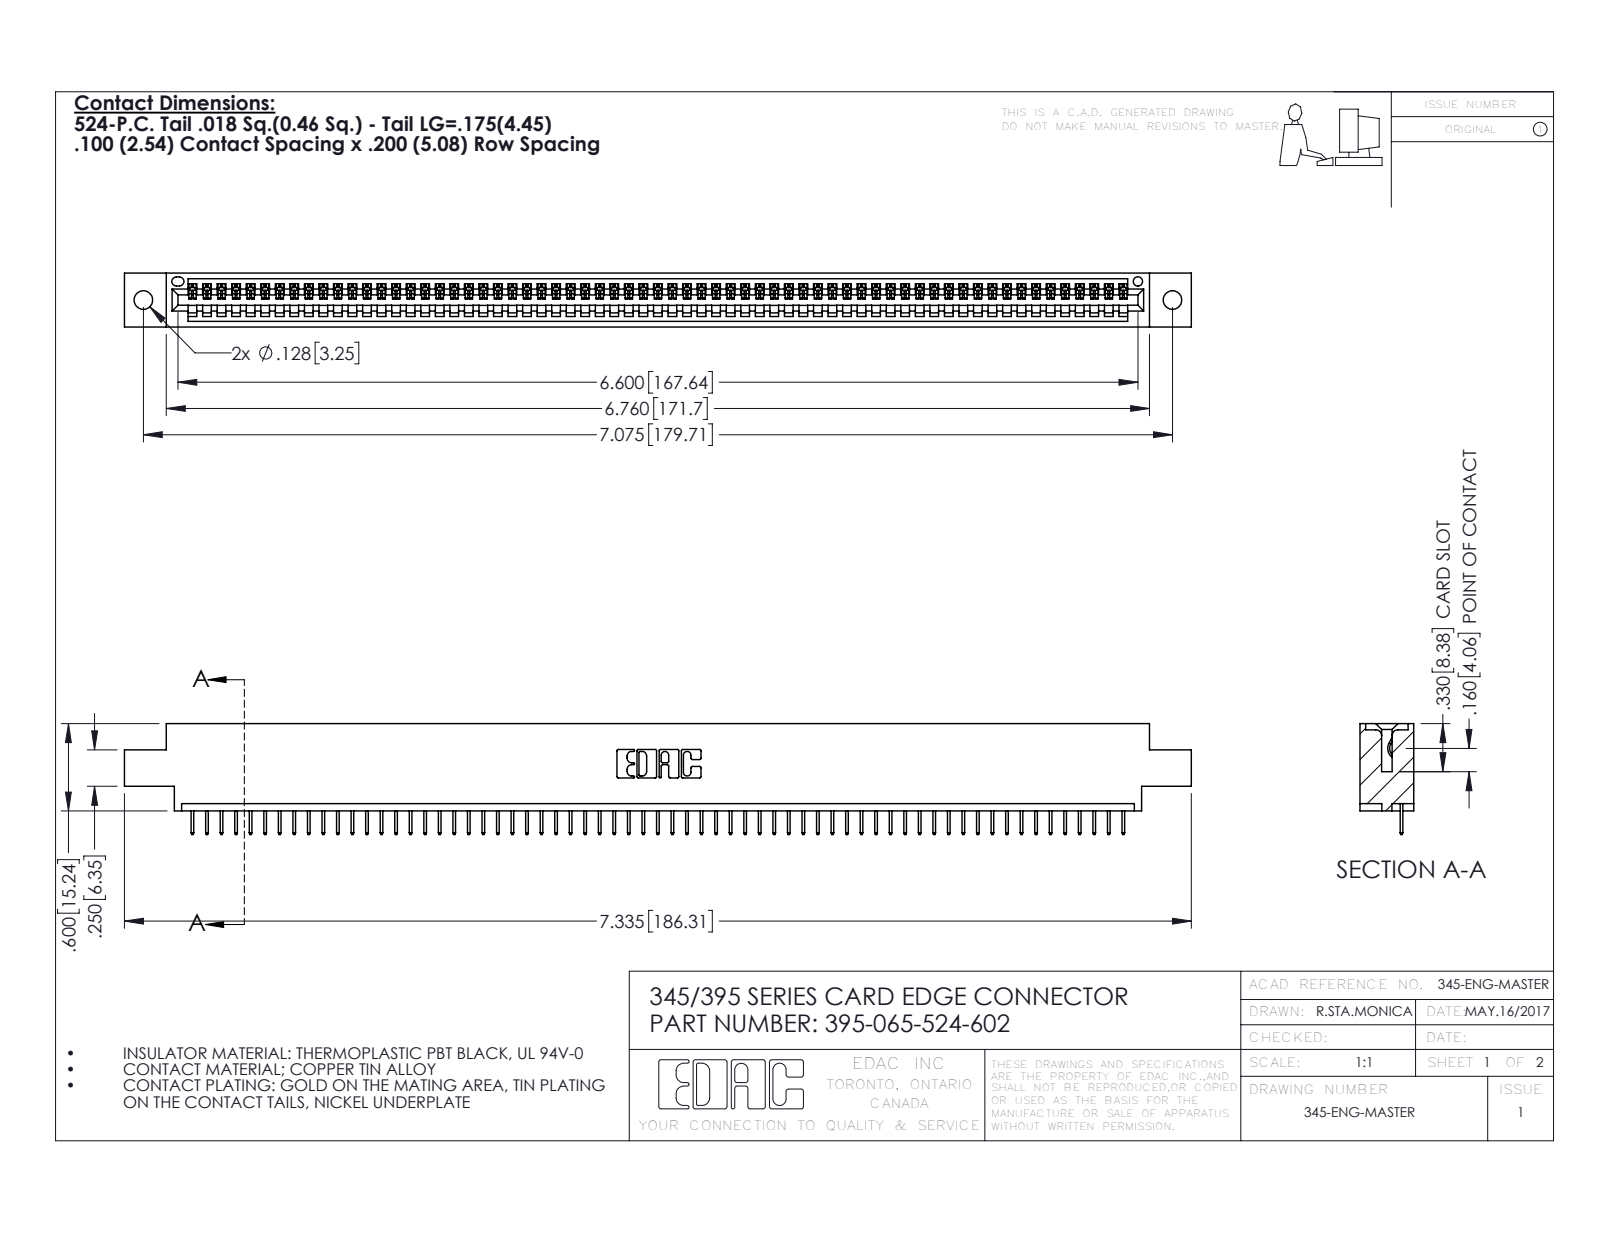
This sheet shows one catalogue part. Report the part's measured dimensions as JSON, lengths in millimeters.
{"part_name": "345-292-001_345-293-124; 395-065-524-602; 345 Part_0.170 Offset - 0.128 Dia", "step_written_by": "SolidWorks 2016 (CONFIG_CONTROL_DESIGN)", "units": "millimeters", "bodies": {"solids": 66, "faces": 4160, "planar": 3074, "cylindrical": 1086, "other": 0}, "overall_size": [186.3, 19.4, 9.4], "volume_mm3": 17480, "surface_area_mm2": 22570, "round_holes": [[3.3, 2], [1.6, 1]], "partial_cylinders_radius": [[0.2, 130], [0.3, 22], [0.2, 6], [0.8, 6], [0.7, 3], [0.8, 2], [1, 2], [0.4, 1]], "face_to_face_distances": [1.8, 7.6, 9.4, 5.1, 2.5, 6.9, 0.6, 5.7, 1.8, 4.4], "hole_center_spacings": [6.9, 173.7, 179.7]}
